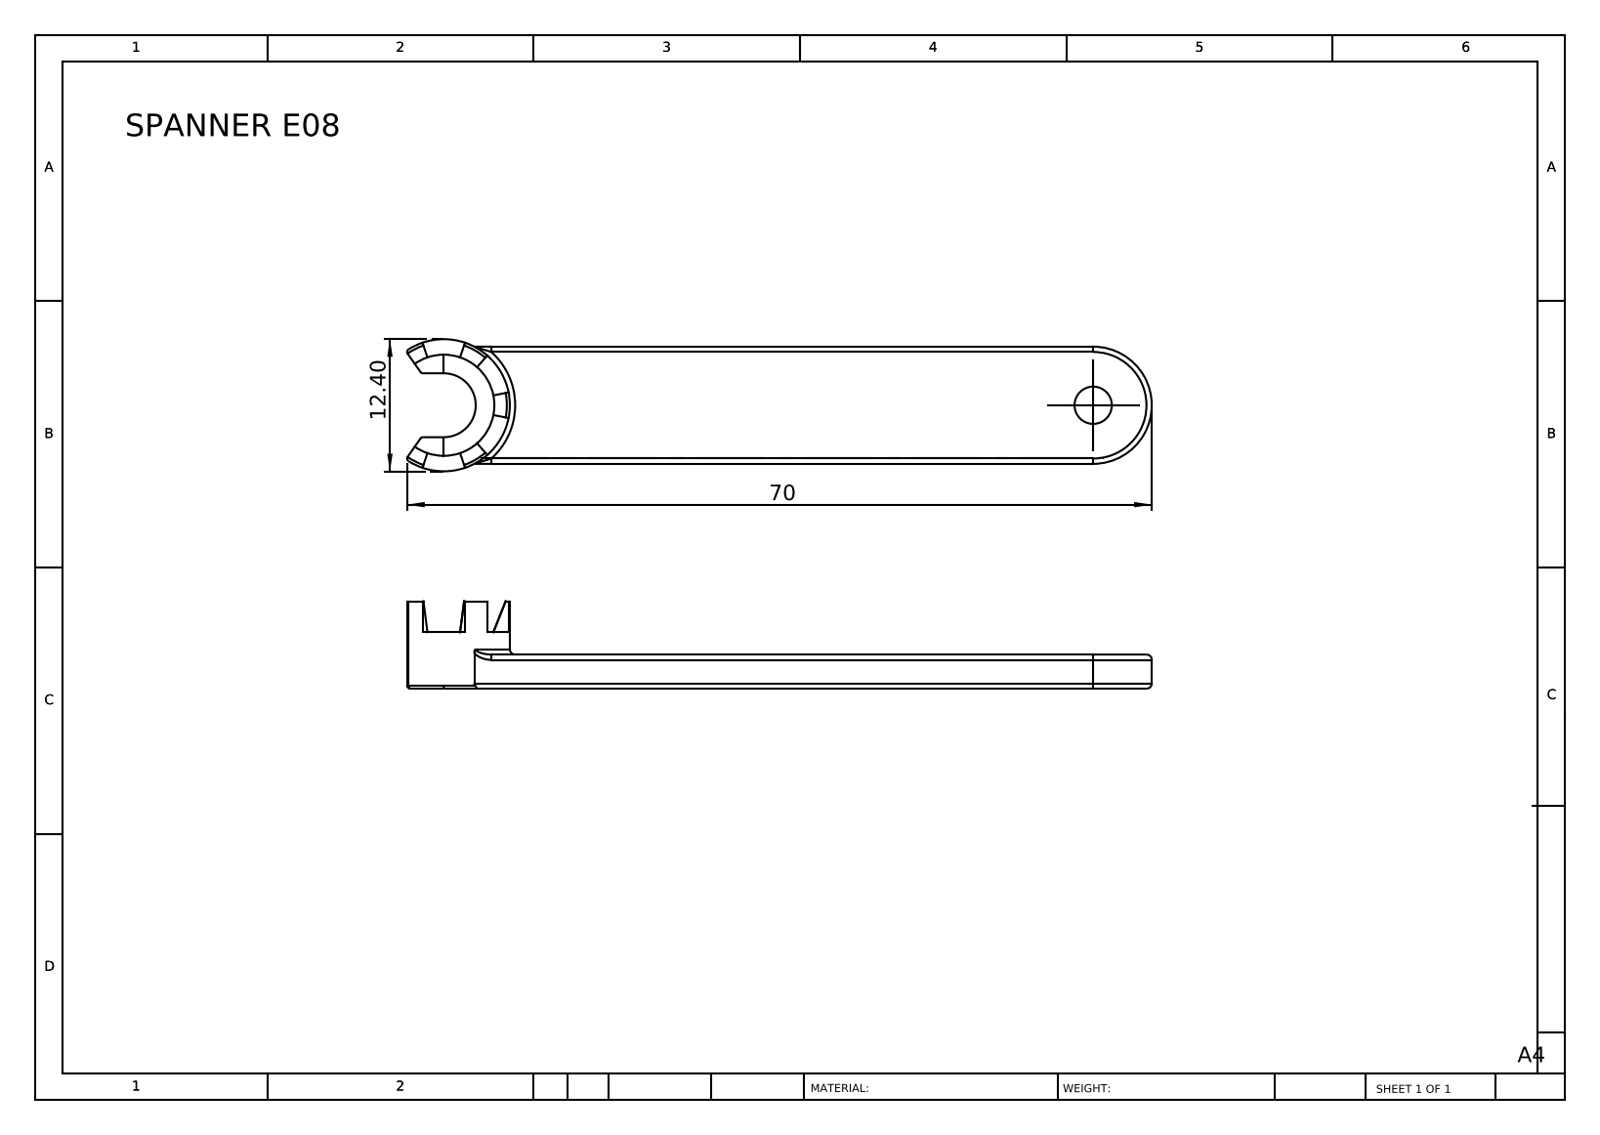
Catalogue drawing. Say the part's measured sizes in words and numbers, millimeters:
The part is named "SPANNER E08M". Its 3-D file was written by "SolidWorks 2014 (CONFIG_CONTROL_DESIGN)". It is 1 solid with 60 faces: 25 planar, 17 cylindrical and 18 other. Overall it measures 69.88 by 12.4 by 8.2 millimeters. Its volume is 2 367 cubic millimeters and its surface area 2 089 square millimeters. Round holes: 1 of diameter 3.5. Partial cylindrical surfaces (rounded edges, fillets, slot ends): 6 of radius 0.3, 4 of radius 0.5, 1 of radius 3, 1 of radius 5.5, 1 of radius 6.2. The main face-to-face distances are 3.2, 11, 2.1, 5.3, 2.5, 8.5, 2.9, 5, 8.2, 6.
